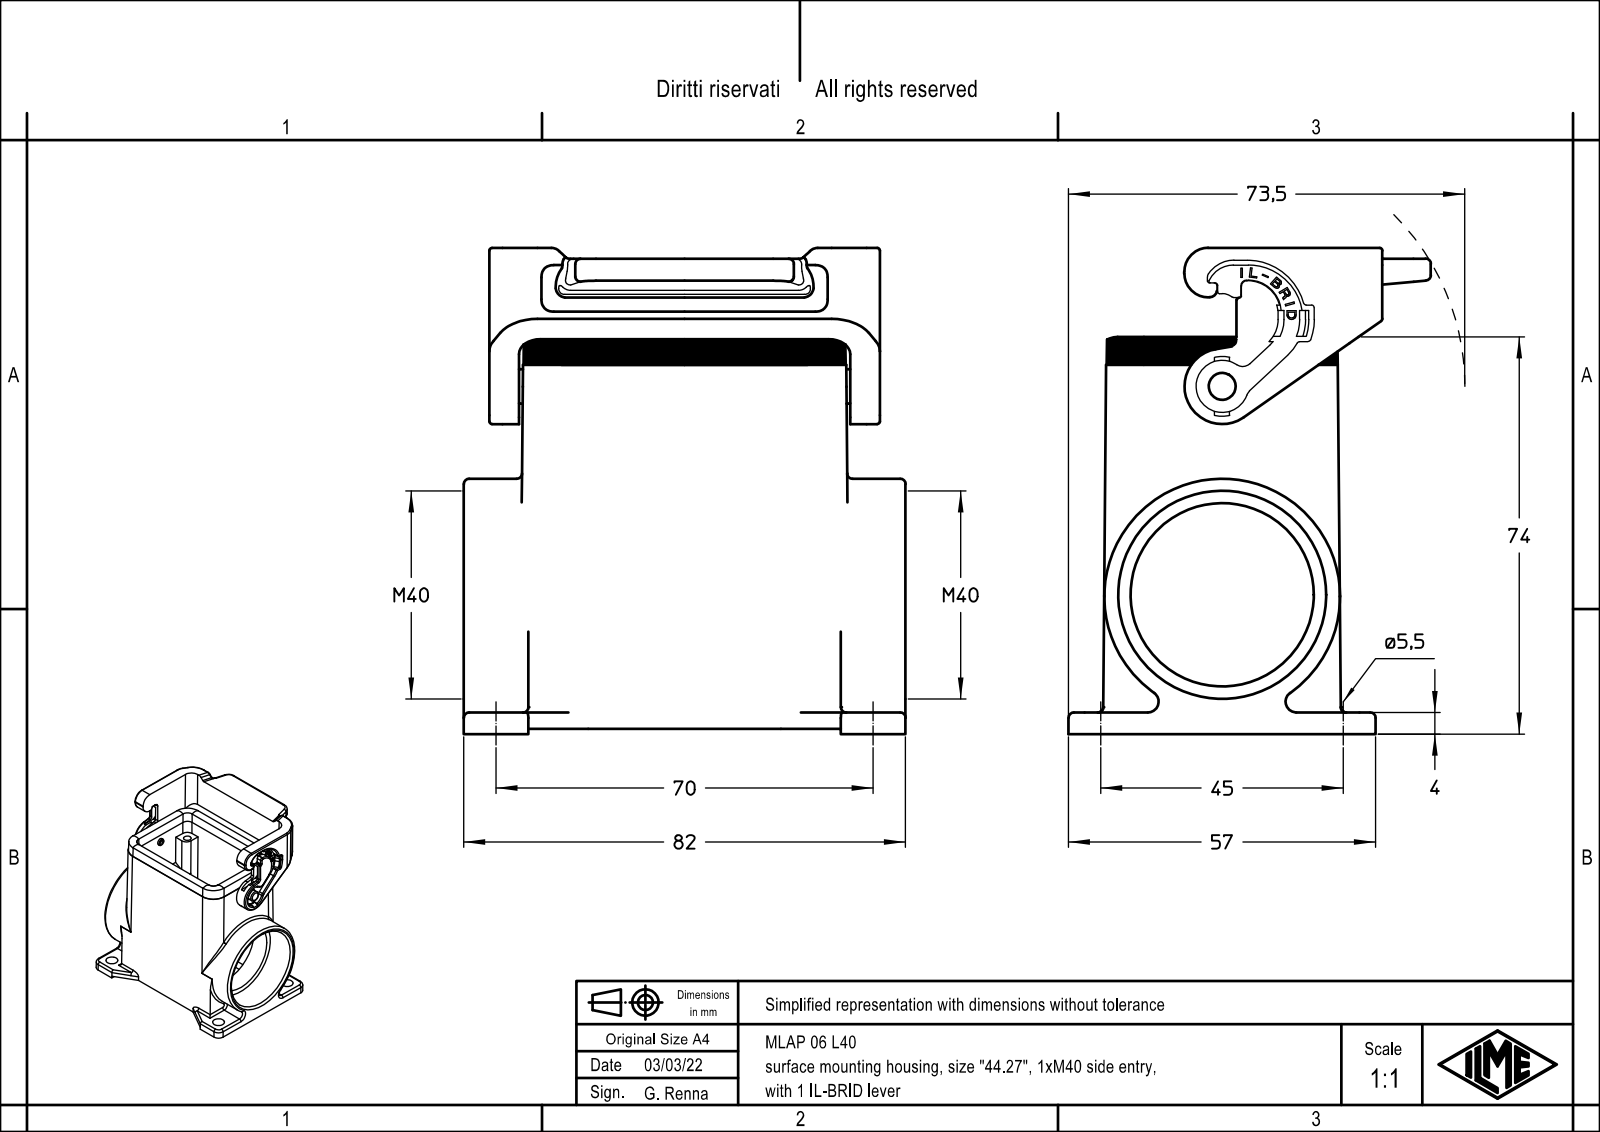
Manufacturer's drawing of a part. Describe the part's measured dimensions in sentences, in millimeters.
The part is named "MLAP_06_L40". Its 3-D file was written by "Creo Elements/Direct Modeling 20.1B 02-Apr-2019 (C) Parametric Technology GmbH (AUTOMOTIVE_DESIGN)". It is 1 solid with 708 faces: 451 planar, 191 cylindrical and 66 other. Overall it measures 90.2 by 82 by 67.25 millimeters. Its volume is 89 645 cubic millimeters and its surface area 46 923 square millimeters. Round holes: 4 of diameter 3.5, 4 of diameter 5.9, 1 of diameter 32, 1 of diameter 34, 1 of diameter 35.7, 1 of diameter 38.6. Round bosses or shafts: 1 of diameter 43, 1 of diameter 6.4, 1 of diameter 4.8. Partial cylindrical surfaces (rounded edges, fillets, slot ends): 31 of radius 1, 16 of radius 3, 10 of radius 1.5, 10 of radius 2, 6 of radius 7, 4 of radius 0.3, 4 of radius 3.1, 4 of radius 4. The main face-to-face distances are 3.75, 39.25, 43, 35.5, 4, 7, 10.25, 3.65, 0.75, 60.75. The hole center spacings are 15.81, 38.28, 57.71, 67.42, 27, 44, 45, 51.62.
